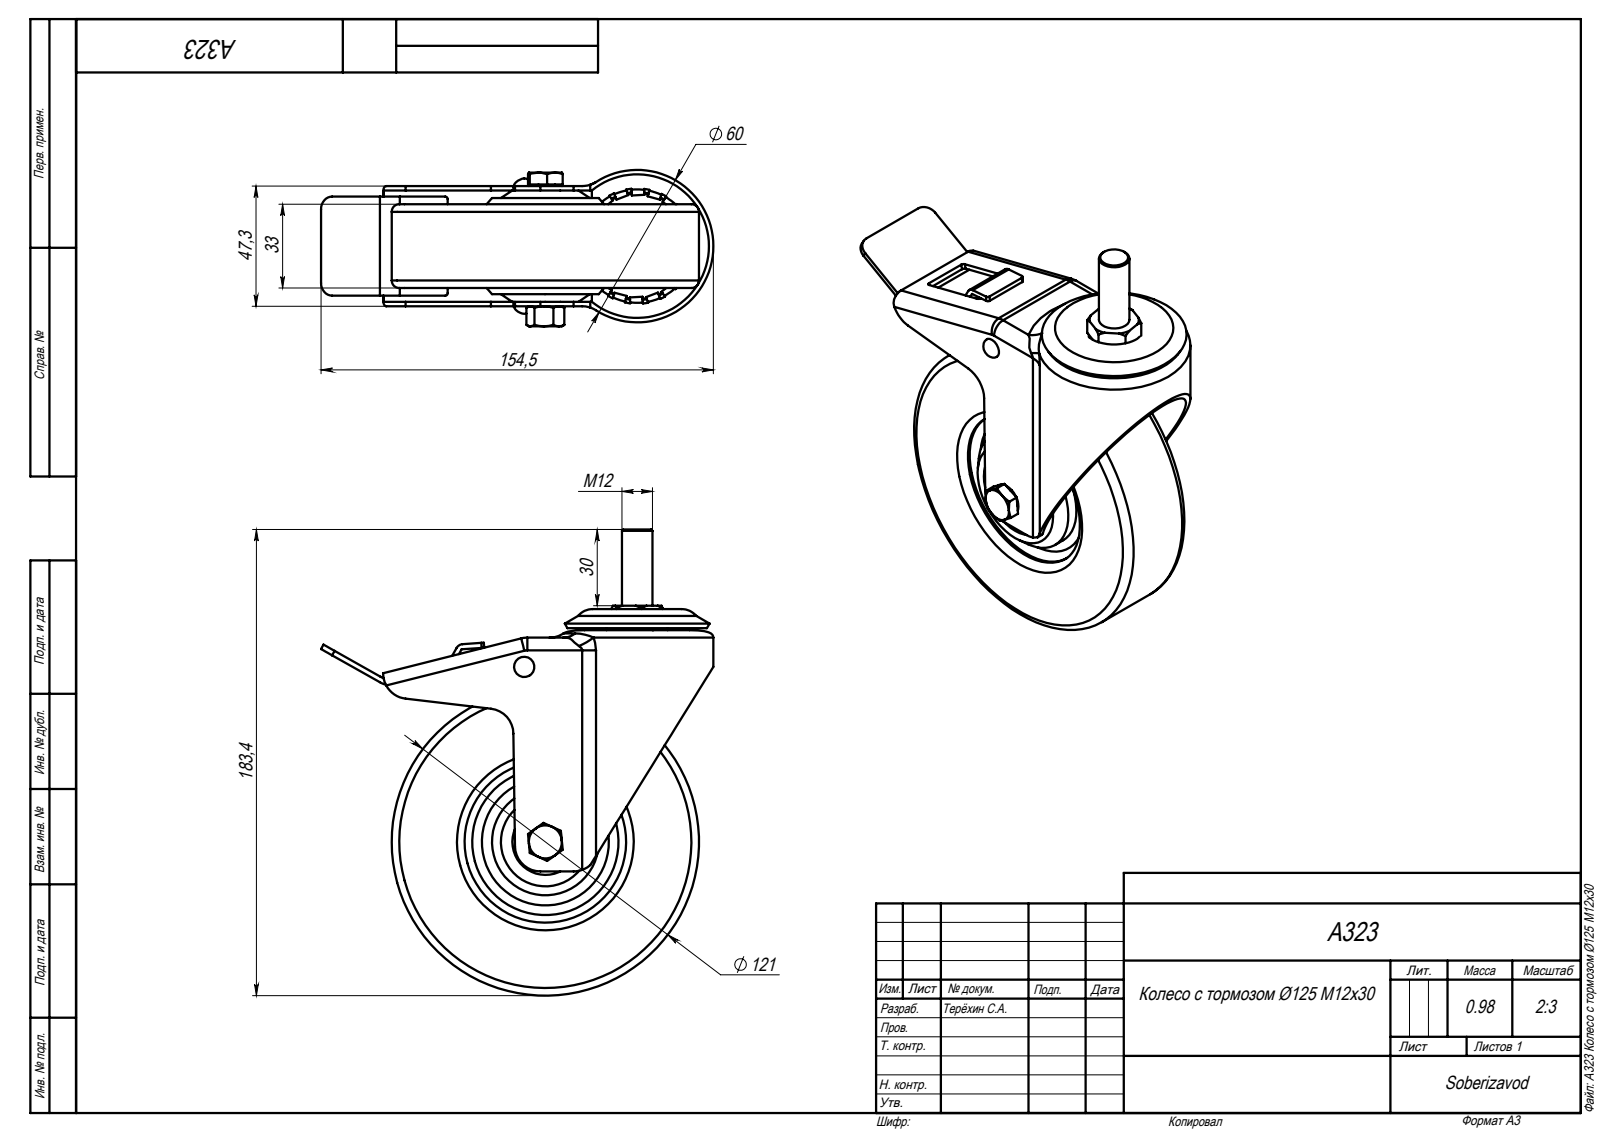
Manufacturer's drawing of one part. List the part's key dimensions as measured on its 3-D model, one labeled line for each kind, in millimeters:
Part name (STEP PRODUCT): hex bolt gradeab_din_DIN EN 24014 - M8 x 55 x 22-N; A323 Колесо с тормозом O125 М12х30; Тормоз_00; Болт_00 (+6 more)
STEP written by: SolidWorks 2018 (AUTOMOTIVE_DESIGN)
Units: millimetres
Bodies: 10 solids, 392 faces (176 planar, 73 cylindrical, 143 other)
Overall size (bounding box): 183.43 × 154.48 × 61.55
Volume: 403 560 mm³ · Surface area: 106 714 mm²
Round holes (diameter × count): ⌀6.8 ×1, ⌀8 ×1, ⌀12 ×1, ⌀46 ×1, ⌀63.6 ×1
Round bosses / shafts (diameter × count): ⌀121 ×1, ⌀50 ×1, ⌀13 ×1
Partial cylindrical surfaces — rounded edges, fillets, slot ends (radius × count): R10 ×9, R1 ×8, R5 ×6, R3 ×1, R28.25 ×1, R30 ×1
Main face-to-face distances: 38.4, 5.4, 33, 1.75, 7.15, 40.15, 45.55, 7, 14.15, 33.15
